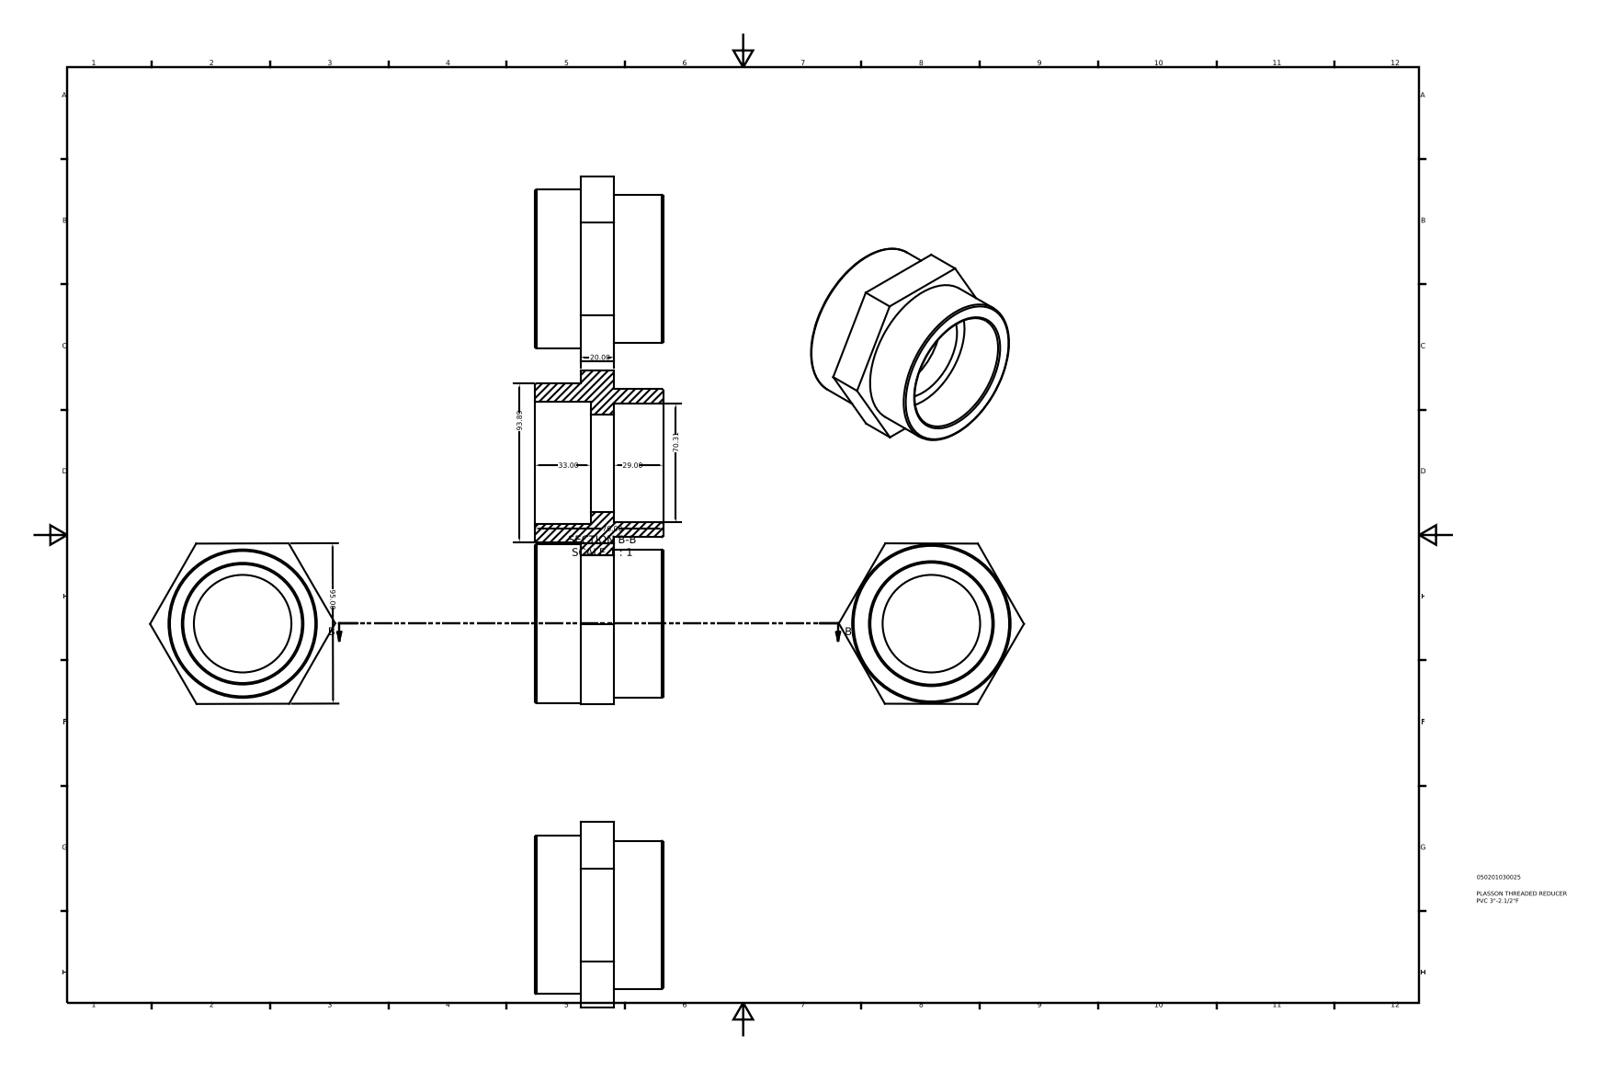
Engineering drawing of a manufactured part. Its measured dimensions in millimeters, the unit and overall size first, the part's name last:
Units: millimetres
Overall size (bounding box): 109.7 × 95.16 × 76
Round holes (diameter × count): ⌀57.78 ×1, ⌀70.31 ×1, ⌀72.23 ×1
Round bosses / shafts (diameter × count): ⌀93.89 ×1, ⌀87.88 ×1
Main face-to-face distances: 47, 95.06, 76, 29, 33, 14, 43, 95, 27, 6
Volume: 234 515 mm³ · Surface area: 48 991 mm²
Bodies: 1 solid, 21 faces (12 planar, 5 cylindrical, 4 other)
Part name (STEP PRODUCT): 050201030025
STEP written by: Autodesk Inventor 2015 (AUTOMOTIVE_DESIGN)
